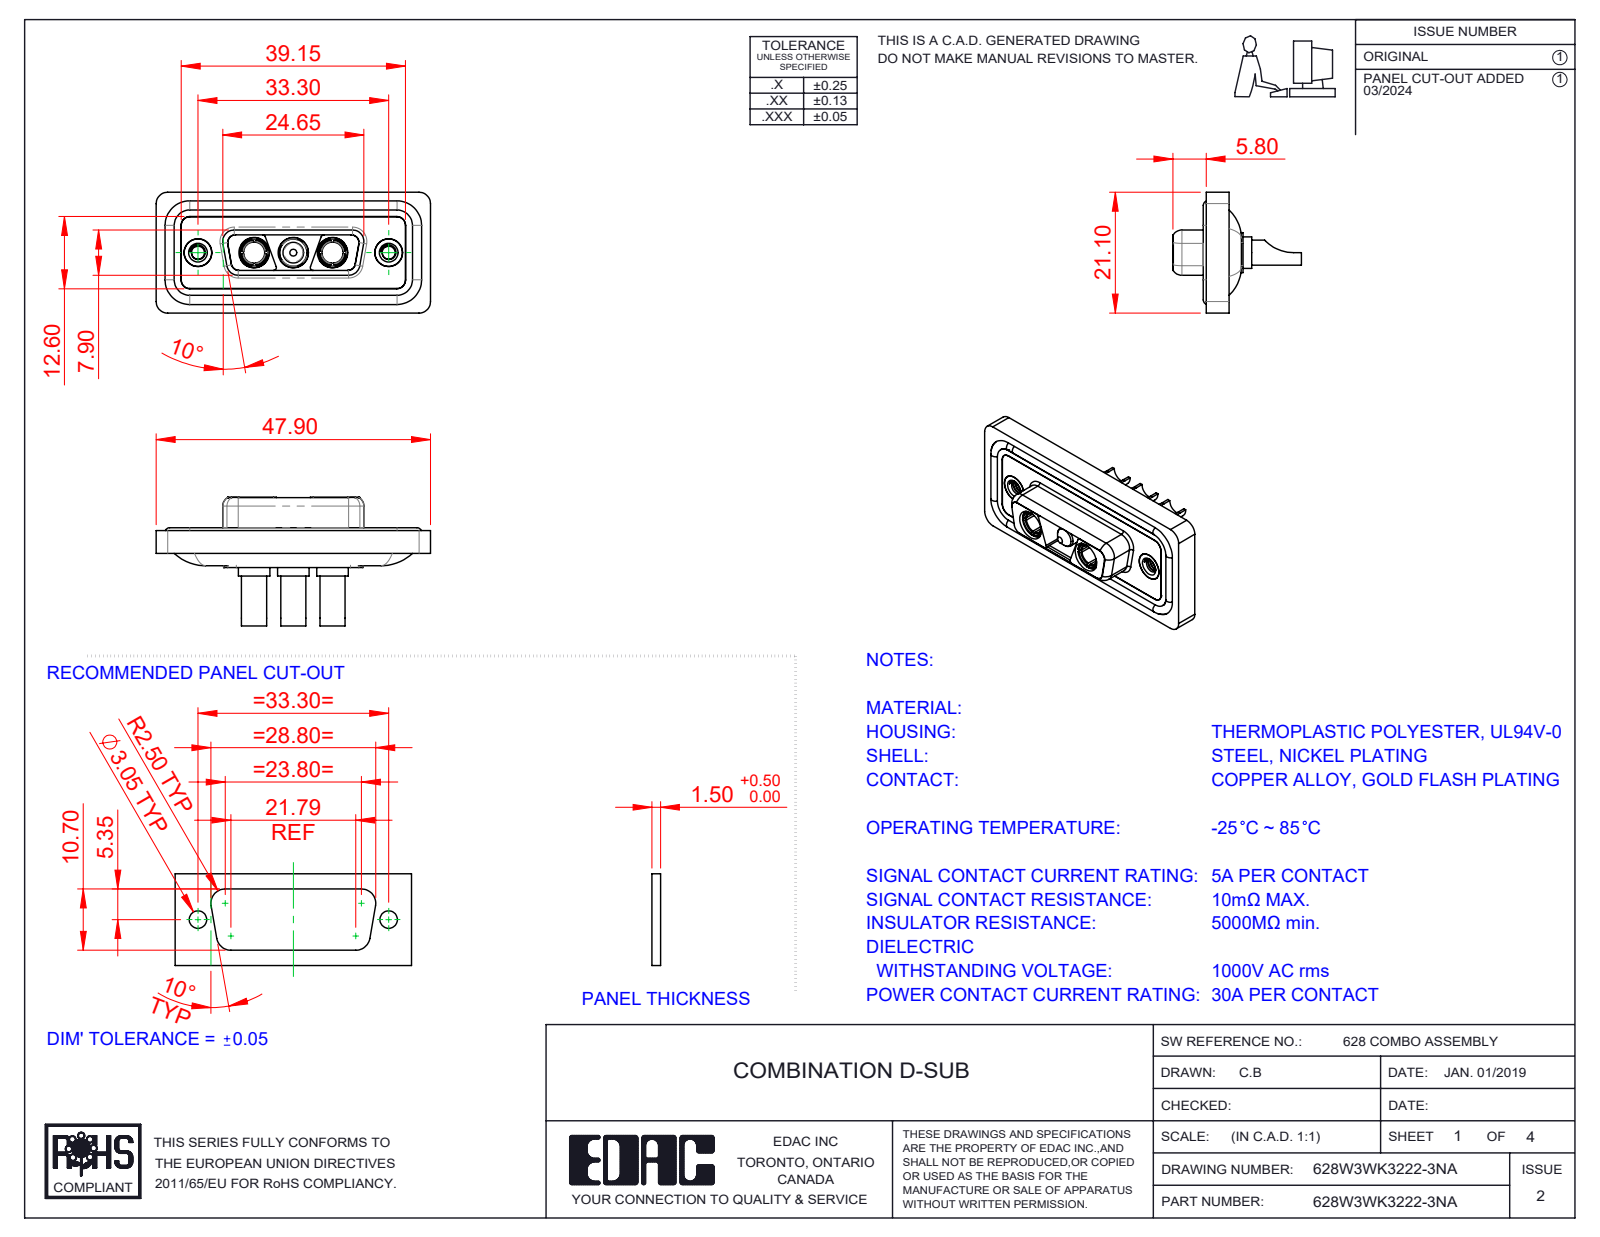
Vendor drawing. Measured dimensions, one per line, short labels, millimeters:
name: Power Socket_30A SC; Power Pin_30A SC; 628W3WK3222-3NA; 628Combo Housing_3WK3 (+4 more)
written by: SolidWorks 2023 (CONFIG_CONTROL_DESIGN)
unit: mm
bodies: 13 solids, 599 faces (187 planar, 269 cylindrical, 143 other)
size: 47.9 × 22.45 × 21.1
volume: 5 952 mm³; area: 9 825 mm²
holes: 5× ⌀4.85, 3× ⌀3.5, 3× ⌀5.3, 2× ⌀2.26, 2× ⌀3.7, 2× ⌀4, 2× ⌀4.05, 2× ⌀5
bosses: 4× ⌀1.6, 3× ⌀5.5, 3× ⌀5.2, 3× ⌀4.75, 3× ⌀4.4, 3× ⌀3.75, 2× ⌀4.96, 2× ⌀4.95
rounds: 22× R1.5, 20× R2, 12× R1.35, 8× R0.5, 8× R1.6, 4× R0.25, 4× R0.6, 4× R0.65
face distances: 0.4, 1.6, 0.5, 1.1, 2.9, 1.8, 5.65, 7.05, 5.35, 6.6
hole spacings: 6.85, 9.8, 16.65, 23.5, 13.7, 33.3
